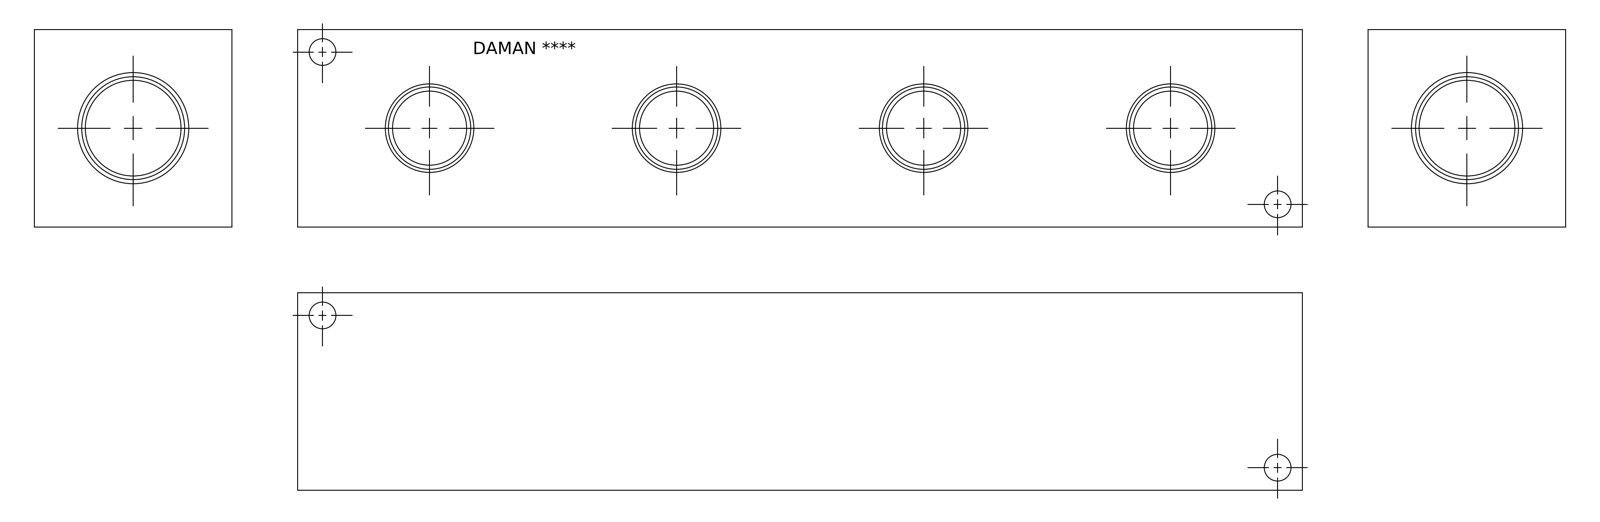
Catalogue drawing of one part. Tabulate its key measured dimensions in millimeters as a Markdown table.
| quantity | value |
| --- | --- |
| part name | Part_AH0000416P_3D |
| STEP written by | Autodesk Inventor 2019 (AUTOMOTIVE_DESIGN) |
| units | millimeters |
| bodies | 1 solid, 338 faces (228 planar, 20 cylindrical, 90 other) |
| overall size | 387.35 × 76.2 × 76.2 |
| volume | 2 083 000 mm³ |
| surface area | 152 979 mm² |
| round holes (diameter × count) | 10.31 × 4, 28.57 × 4, 33.71 × 4, 36.91 × 1, 42.47 × 1 |
| main face-to-face distances | 76.2, 387.35, 57.2, 19, 19.51, 367.84, 348.33, 75.2, 18, 1 |
| hole center spacings | 95.25, 50.65, 139.64, 190.5, 233.62, 328.34, 372.94, 285.75 |
